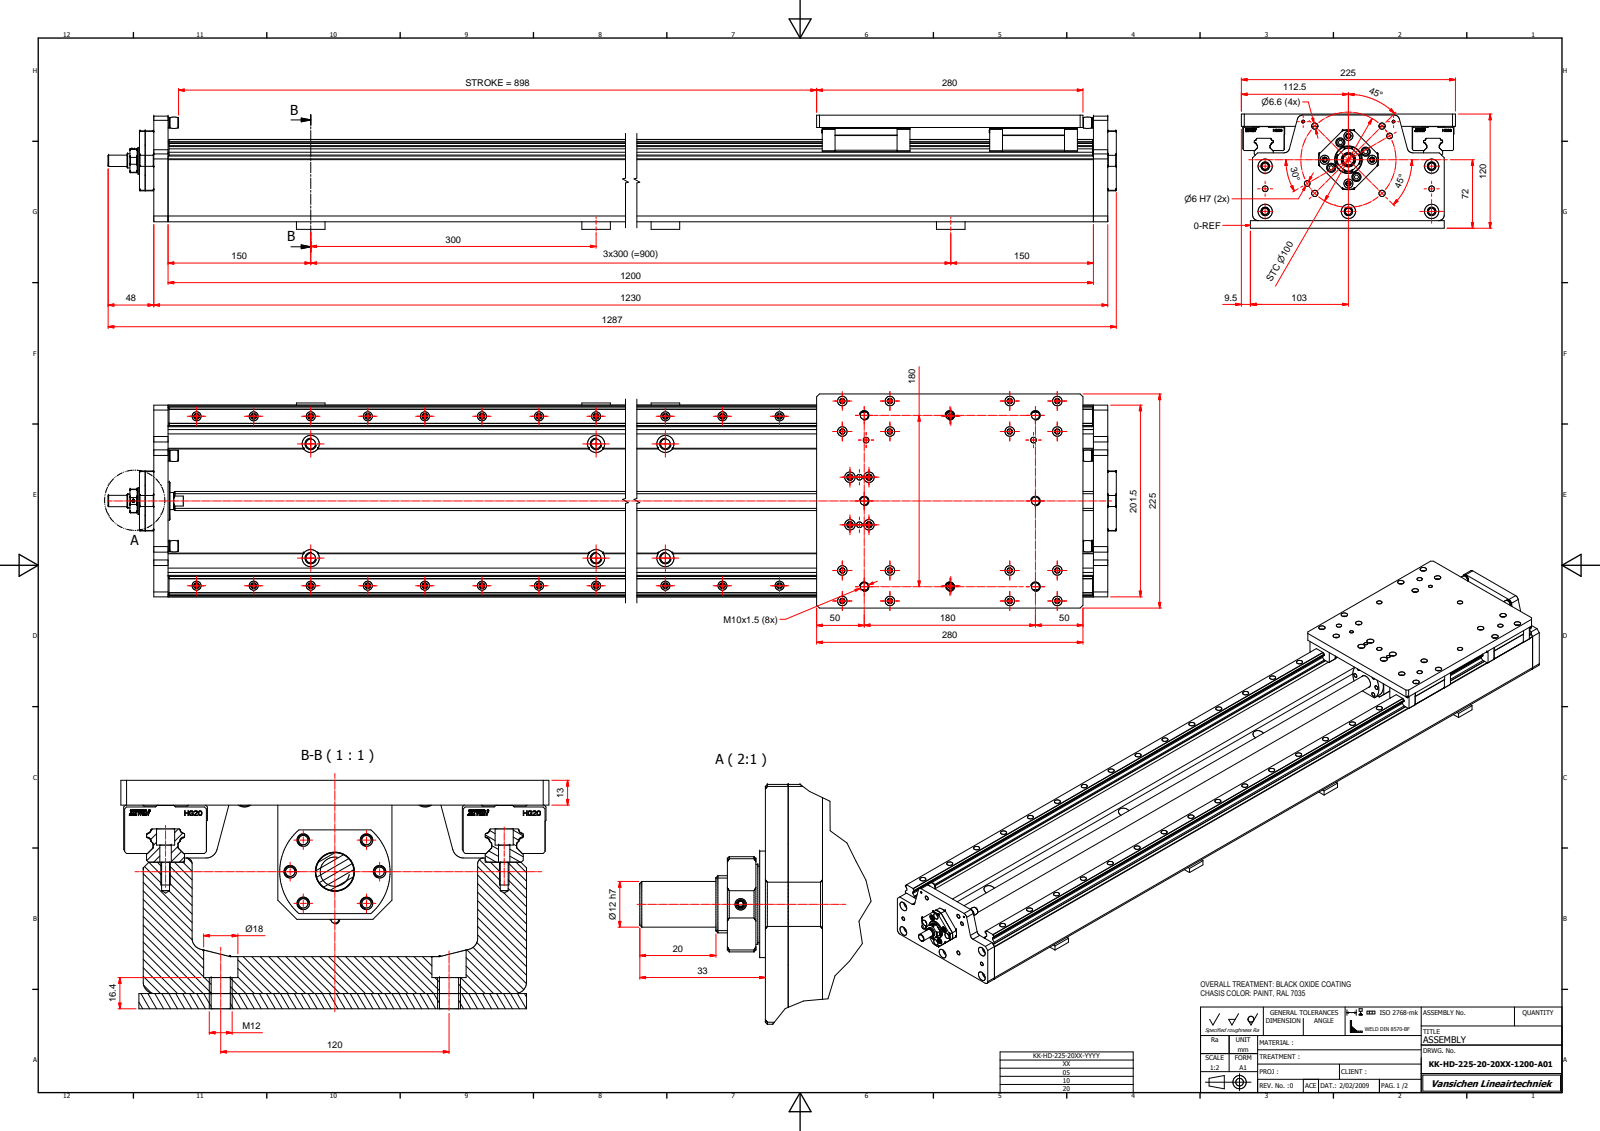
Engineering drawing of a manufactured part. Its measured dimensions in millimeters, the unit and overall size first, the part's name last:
Units: millimetres
Overall size (bounding box): 1287 × 225 × 120
Round holes (diameter × count): ⌀6 ×50, ⌀9.5 ×48, ⌀4.13 ×44, ⌀5.5 ×20, ⌀5 ×16, ⌀10 ×16, ⌀6.6 ×14, ⌀8.38 ×8, ⌀10.11 ×8, ⌀11 ×8, ⌀18 ×8, ⌀4.92 ×6
Round bosses / shafts (diameter × count): ⌀7.5 ×4, ⌀11 ×2, ⌀5.5 ×2, ⌀3 ×2, ⌀36 ×1, ⌀32 ×1, ⌀28 ×1, ⌀21 ×1
Partial cylindrical surfaces — rounded edges, fillets, slot ends (radius × count): R0.5 ×22, R1 ×16, R6 ×10, R2.03 ×8, R2.3 ×8, R3 ×4, R12.5 ×1, R29 ×1
Main face-to-face distances: 19.4, 25.7, 175.8, 201.5, 112, 92.6, 13, 99, 79.6, 150.1
Hole centre spacings: 50, 69.95, 18.61, 36.85, 44.82, 55.25, 90, 201.25
Volume: 10 890 000 mm³ · Surface area: 1 303 000 mm²
Bodies: 1 solid, 2486 faces (1603 planar, 495 cylindrical, 388 other)
STEP written by: Autodesk Inventor 2008 (AUTOMOTIVE_DESIGN)
